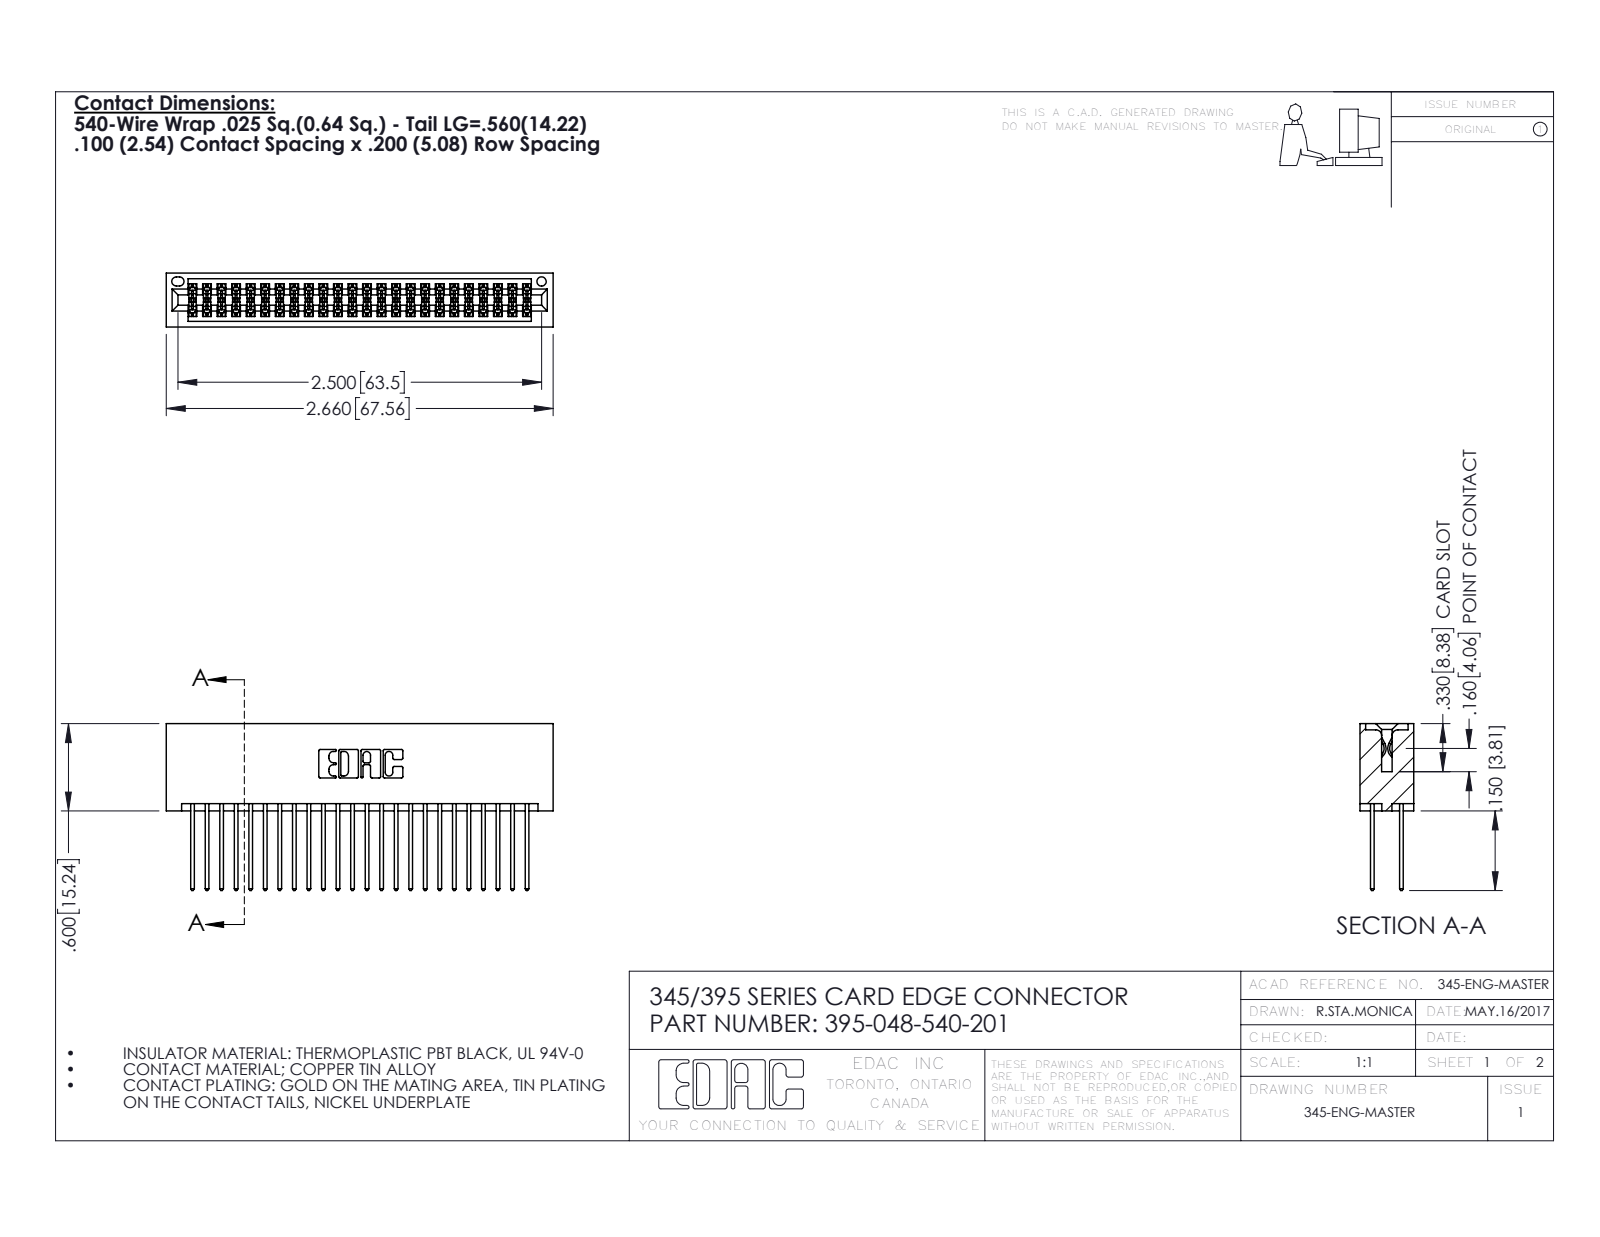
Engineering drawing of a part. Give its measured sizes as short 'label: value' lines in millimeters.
name: 345 Part_No Mounting Lugs; 345-292-001_345-293-140; 395-048-540-201
written by: SolidWorks 2016 (CONFIG_CONTROL_DESIGN)
unit: mm
bodies: 49 solids, 2518 faces (1660 planar, 858 cylindrical, 0 other)
size: 67.6 × 29.1 × 9.4
volume: 7 190 mm³; area: 11 430 mm²
holes: 1× ⌀1.6
rounds: 72× R0.2, 48× R0.3, 22× R0.3, 6× R0.2, 6× R0.8, 3× R0.7, 2× R0.4, 2× R0.5
face distances: 7.6, 1.8, 5.1, 2.5, 6.9, 0.6, 9.4, 5.7, 4.4, 3.8
